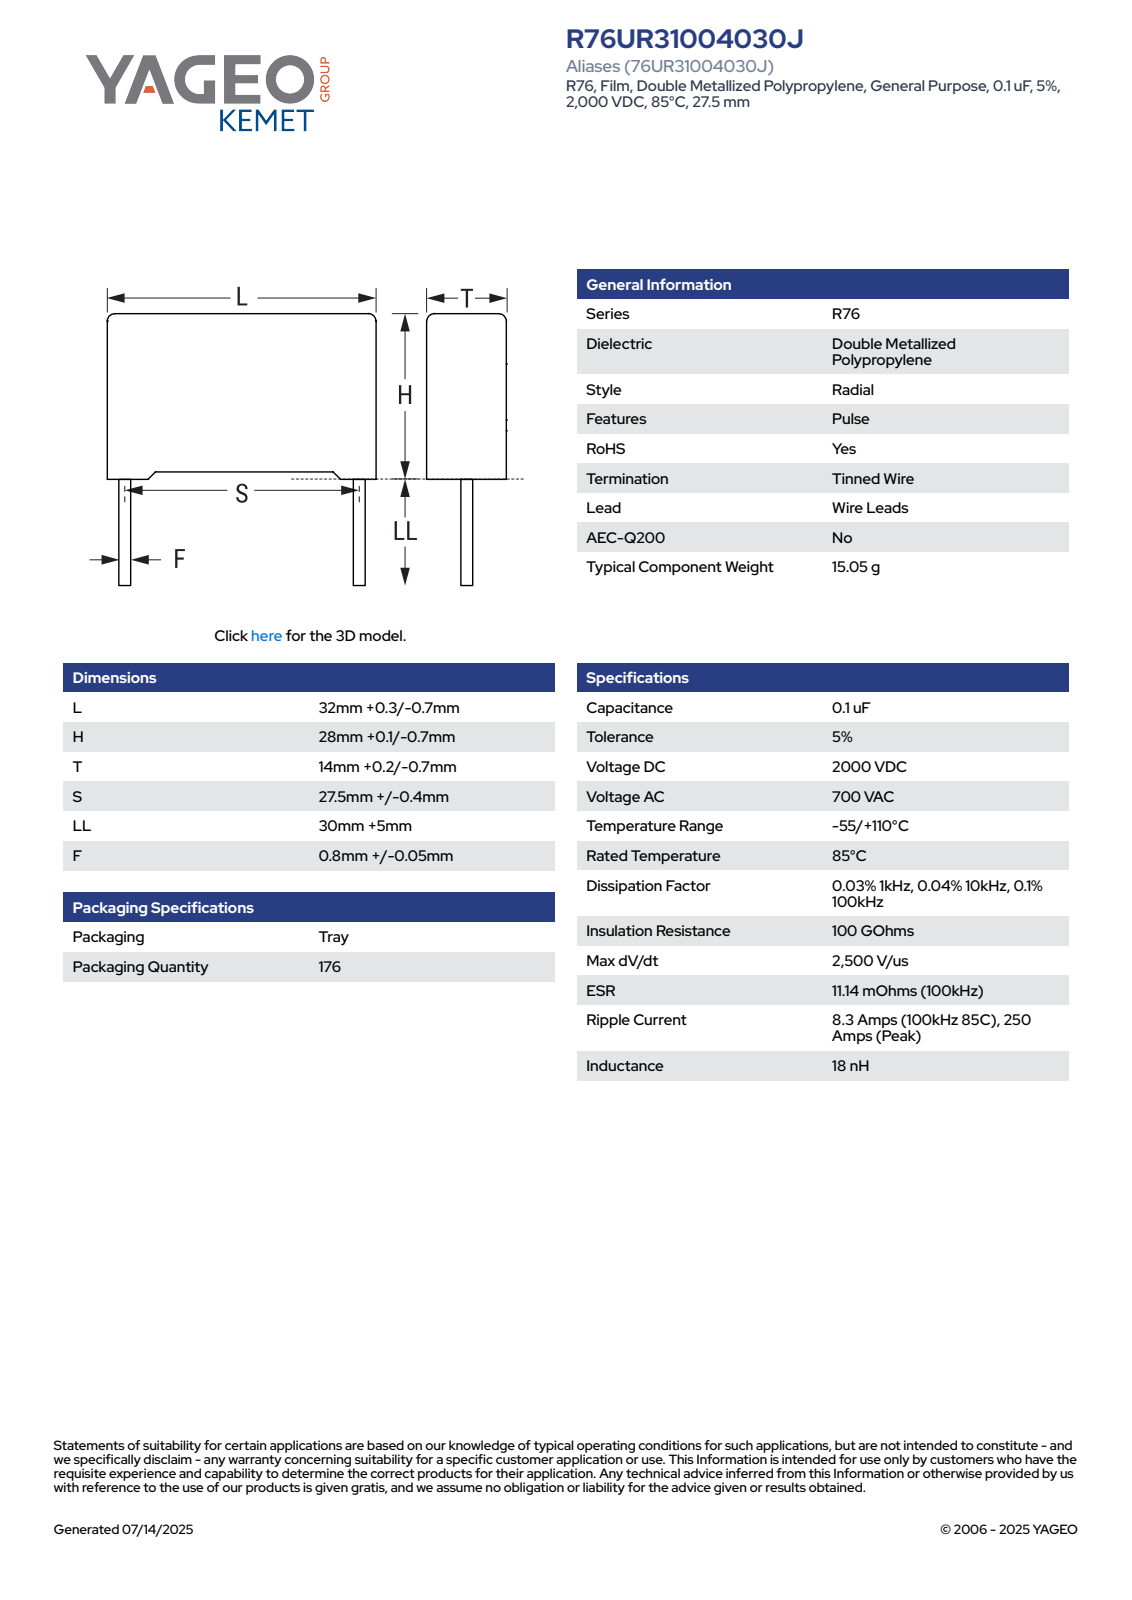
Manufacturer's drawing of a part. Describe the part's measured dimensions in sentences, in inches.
The part is named "CFR_RB2_32X28X14_L32.3H28.1T14.2S27.5LL35F0.85". Its 3-D file was written by "SolidWorks 2021 (AUTOMOTIVE_DESIGN)". It is 4 solids with 85 faces: 77 planar, 8 cylindrical and 0 other. Overall it measures 2.484 by 1.272 by 0.559 inches. Its volume is 0.765 cubic inches and its surface area 5.837 square inches. Round bosses or shafts: 2 of diameter 0.033. Partial cylindrical surfaces (rounded edges, fillets, slot ends): 4 of radius 0.02. The main face-to-face distances are 0.559, 1.272, 1.068, 1.077, 0.03, 0.038, 1.106, 0.043, 1.229, 0.517.
